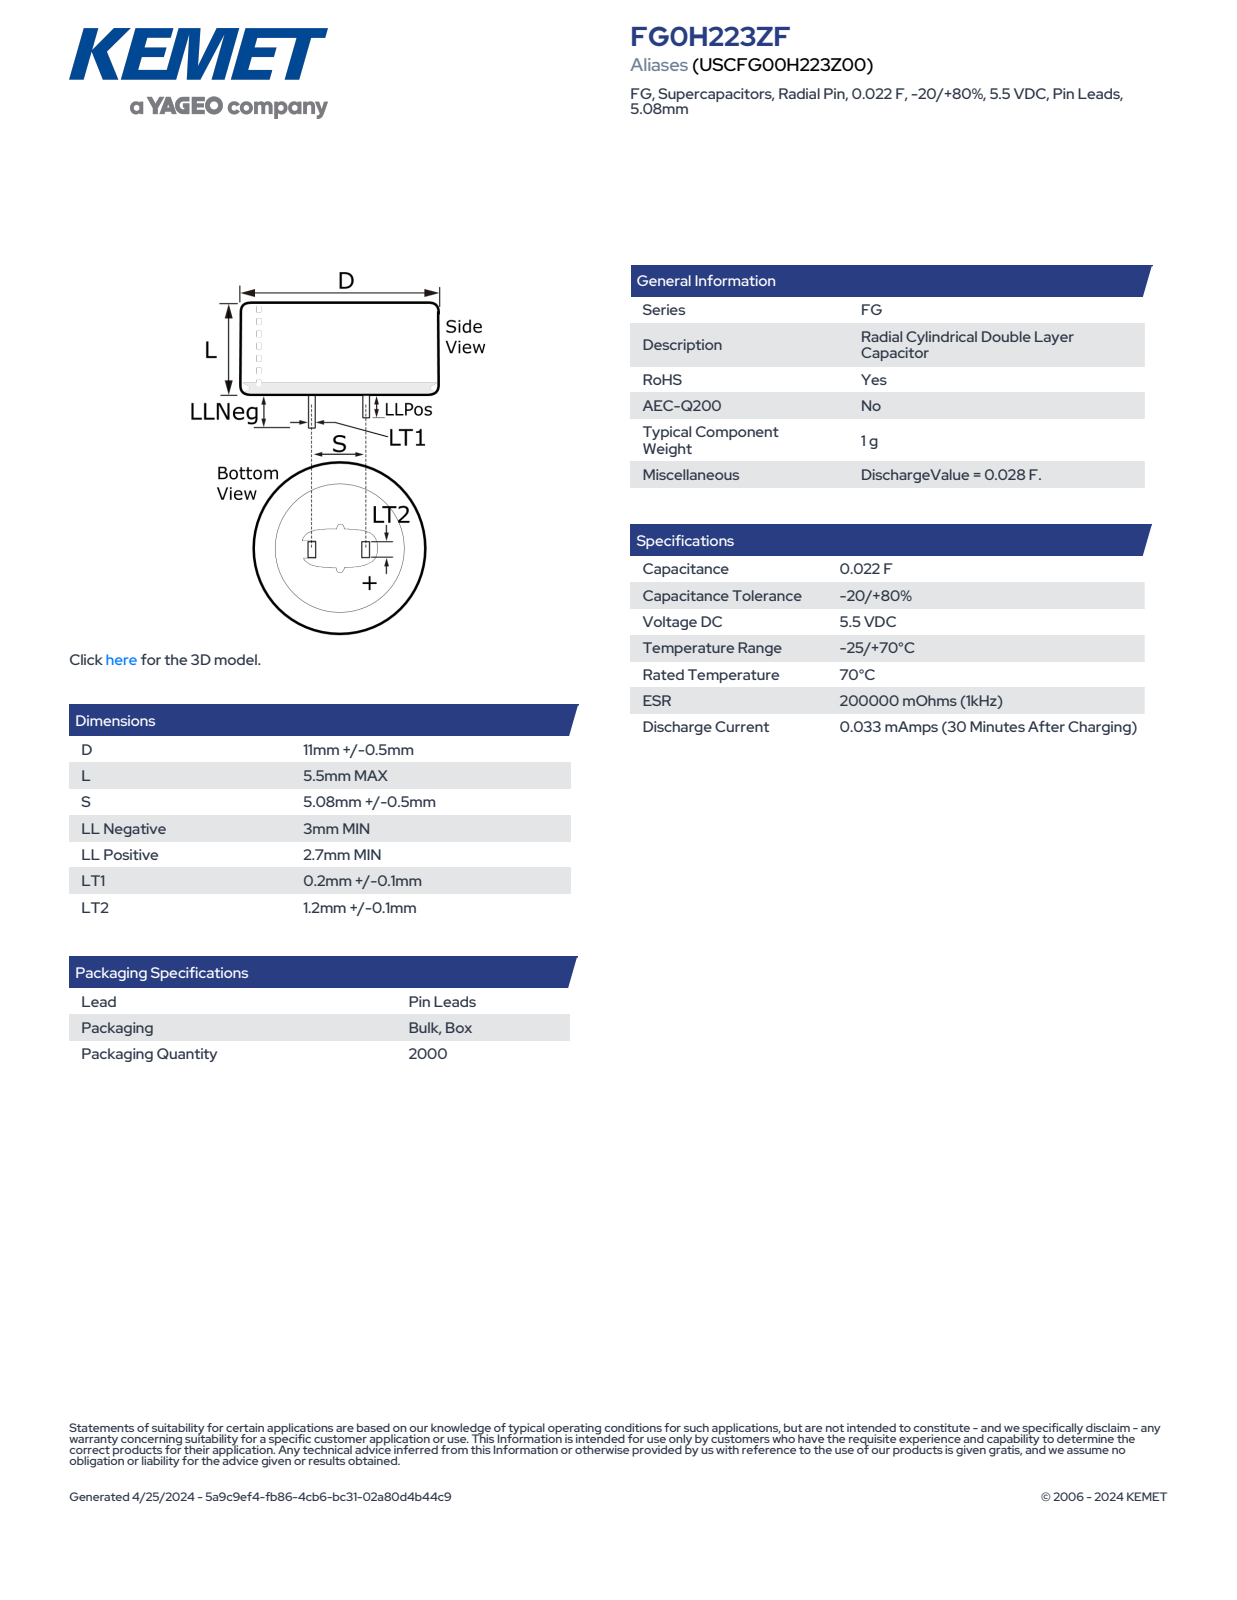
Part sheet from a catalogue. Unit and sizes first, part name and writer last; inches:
Units: inches
Overall size (bounding box): 0.453 × 0.453 × 0.335
Round bosses / shafts (diameter × count): ⌀0.453 ×1
Partial cylindrical surfaces — rounded edges, fillets, slot ends (radius × count): R0.227 ×1
Main face-to-face distances: 0.217, 0.2, 0.212, 0.188, 0.051, 0.118, 0.335, 0.106, 0.323, 0.014
Volume: 0.035 in³ · Surface area: 0.642 in²
Bodies: 1 solid, 78 faces (70 planar, 4 cylindrical, 4 other)
Part name (STEP PRODUCT): CDR_LPLLN_D11.5L5.5S5.08LLNEG3LLPOS2.7LT10.3LT21.3
STEP written by: SolidWorks 2014 (AUTOMOTIVE_DESIGN)
